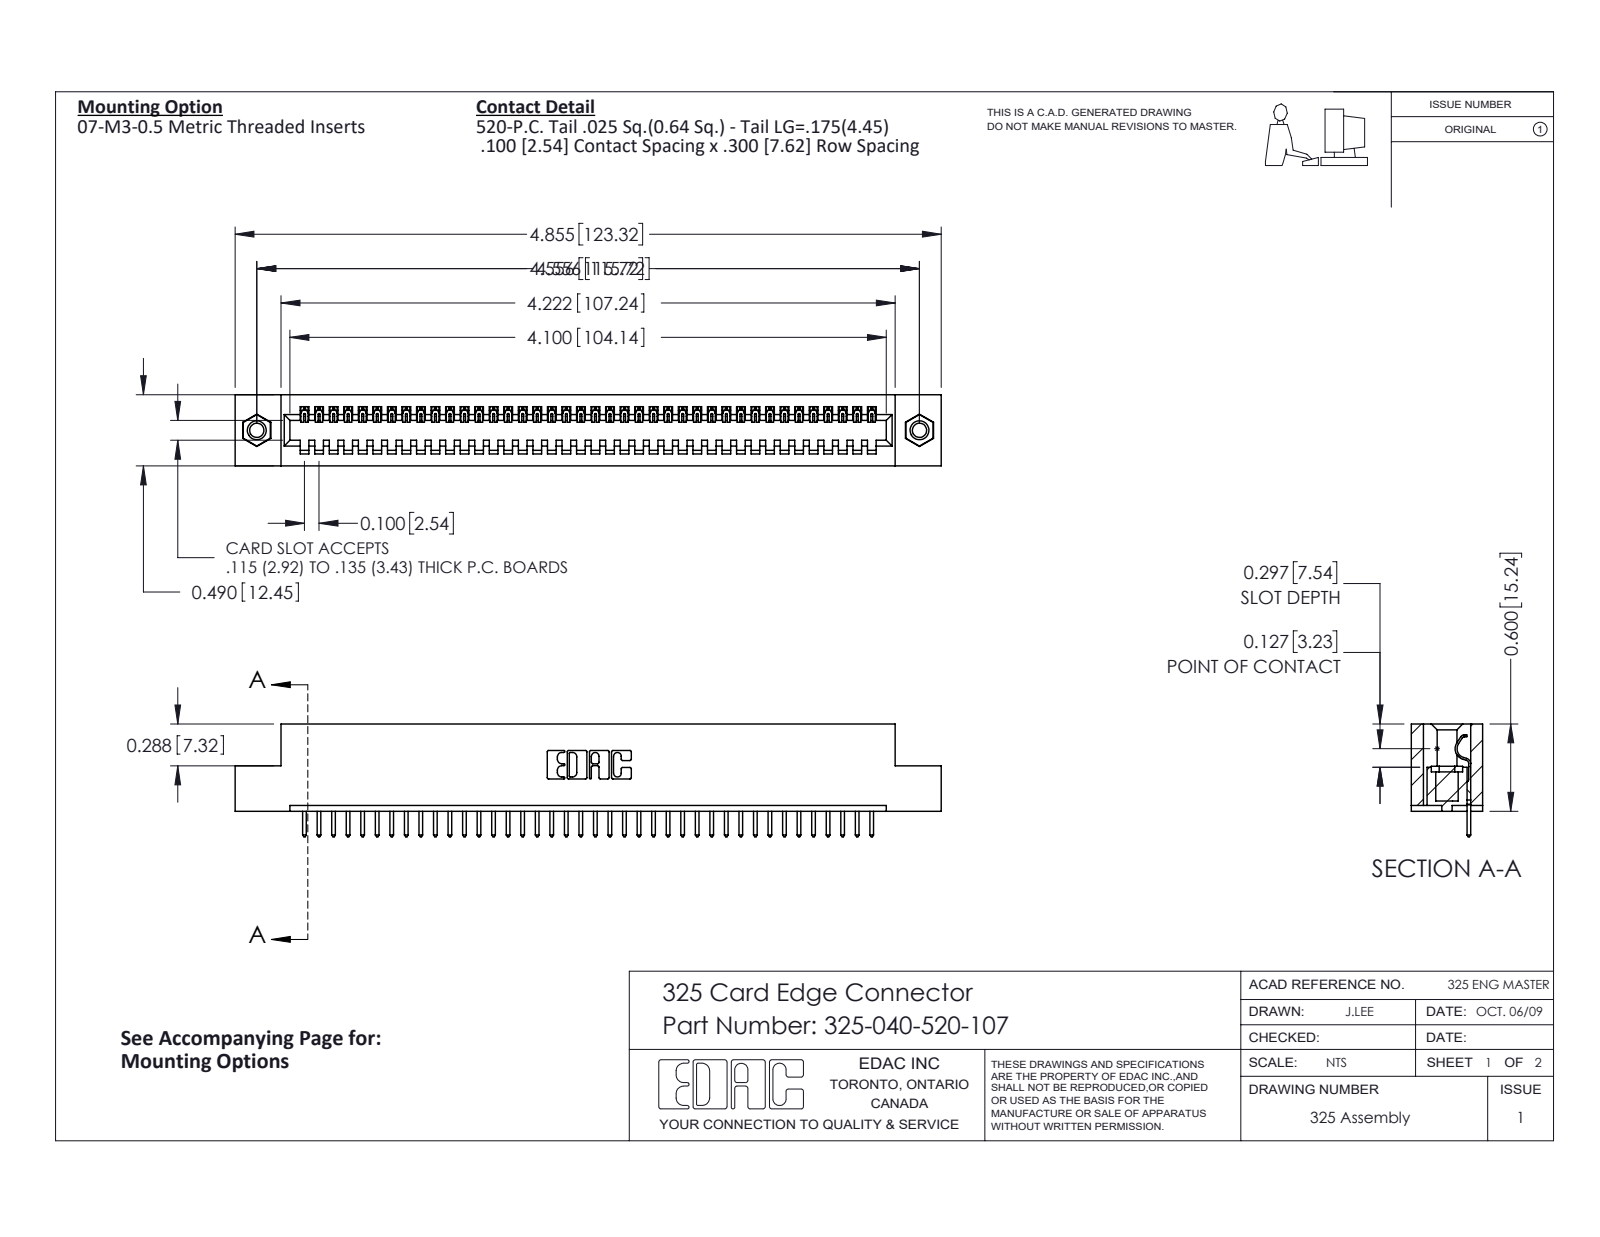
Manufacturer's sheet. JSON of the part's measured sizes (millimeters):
{"part_name": "345-250-001_345-250-005-103; 325 Part_TI; 325-292-001_325-293-120; 325-040-520-107", "step_written_by": "SolidWorks 2016 (CONFIG_CONTROL_DESIGN)", "units": "millimeters", "bodies": {"solids": 43, "faces": 2494, "planar": 1782, "cylindrical": 696, "other": 16}, "overall_size": [123.3, 19.7, 12.4], "volume_mm3": 15500, "surface_area_mm2": 16530, "round_holes": [[2.5, 2], [3.2, 2], [4.1, 2]], "round_bosses_or_shafts": [[3.9, 2]], "partial_cylinders_radius": [[0.2, 80], [0.3, 80], [0.3, 22], [0.2, 6], [0.8, 6], [0.7, 3], [0.4, 1], [0.6, 1]], "face_to_face_distances": [2.1, 10.3, 12.4, 7.6, 2.7, 9.7, 0.6, 8.3, 14.2, 6.7], "hole_center_spacings": [115.7]}
